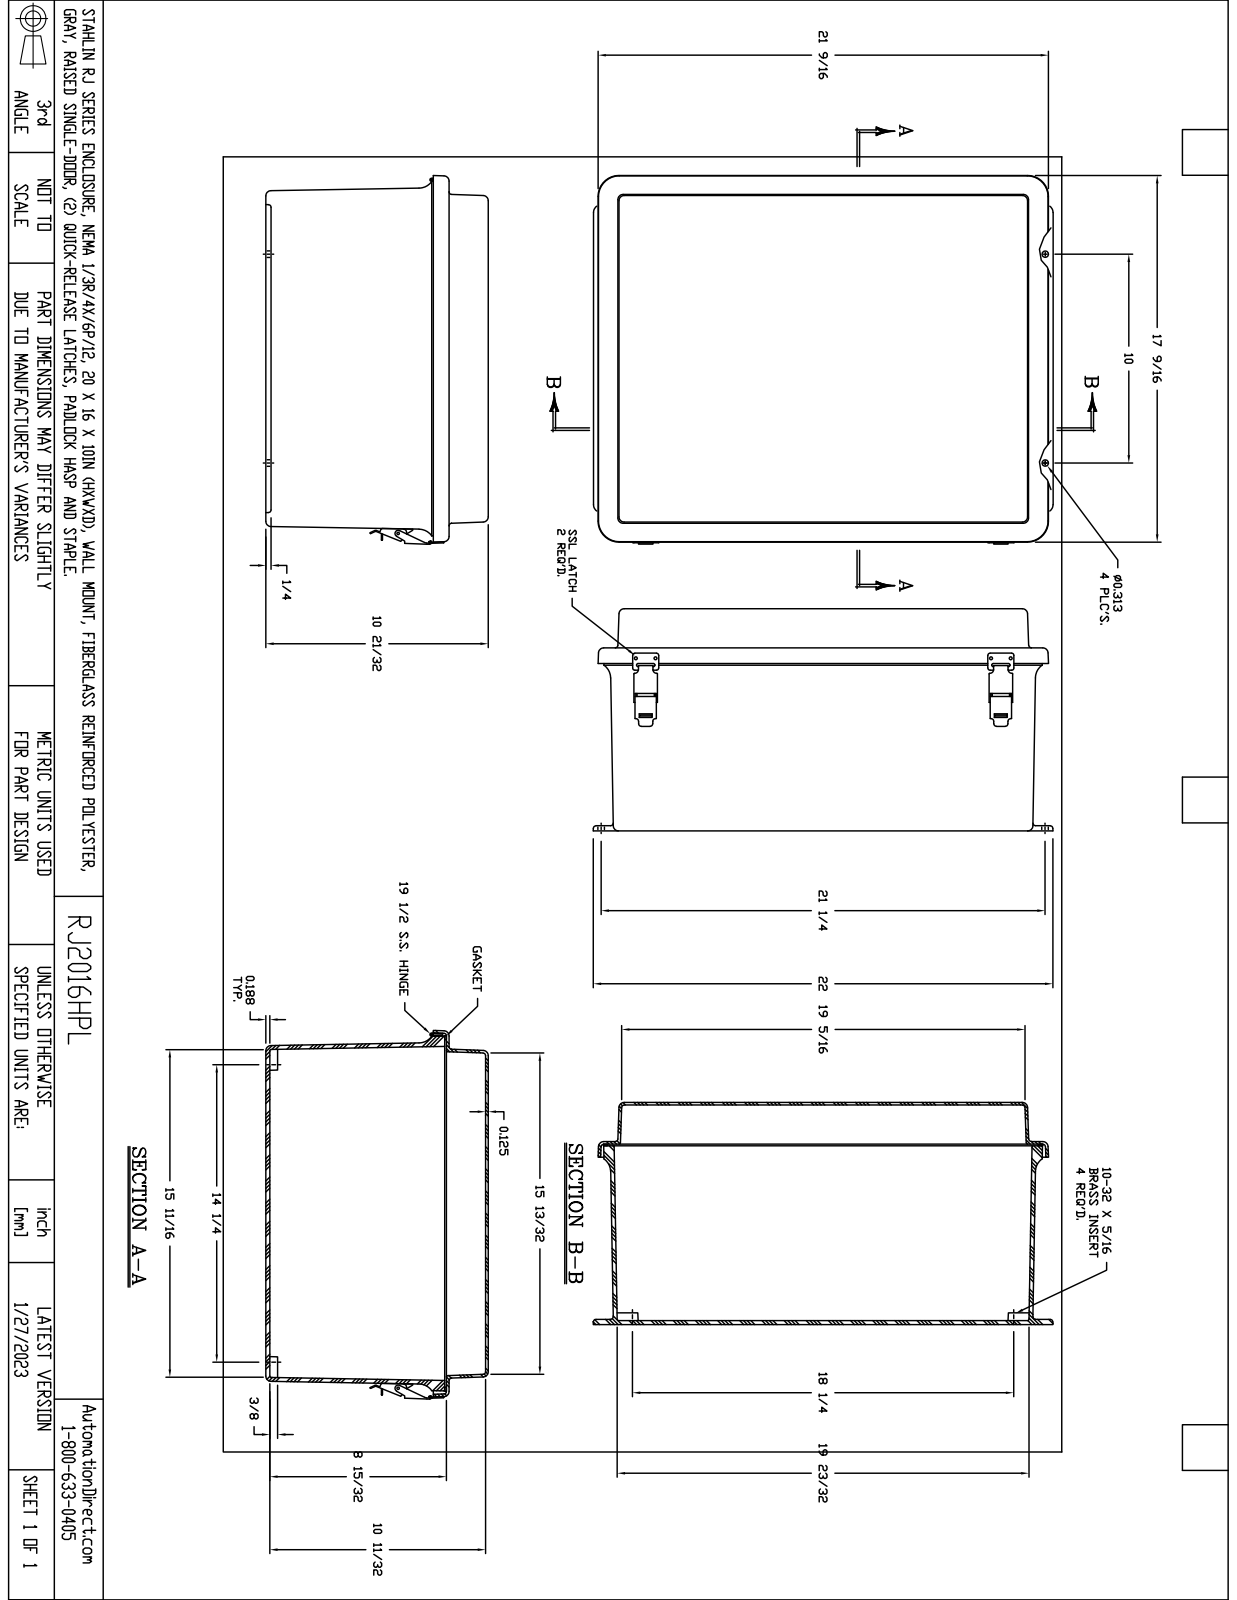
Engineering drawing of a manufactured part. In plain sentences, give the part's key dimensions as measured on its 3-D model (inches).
The part is named "MR2016HPL". Its 3-D file was written by "SolidWorks 2018 (AUTOMOTIVE_DESIGN)". It is 42 solids with 1215 faces: 543 planar, 505 cylindrical and 167 other. Overall it measures 22 by 17.698 by 10.642 inches. Its volume is 271.4 cubic inches and its surface area 3 192 square inches. Round holes: 24 of diameter 0.14, 12 of diameter 0.131, 8 of diameter 0.104, 5 of diameter 0.152, 4 of diameter 0.13, 4 of diameter 0.156, 4 of diameter 0.218, 2 of diameter 0.135, 2 of diameter 0.375, 1 of diameter 0.085, 1 of diameter 0.135. Round bosses or shafts: 14 of diameter 0.125, 12 of diameter 0.25, 6 of diameter 0.125, 4 of diameter 0.27, 1 of diameter 0.3, 1 of diameter 0.17, 1 of diameter 0.155, 1 of diameter 0.12. Partial cylindrical surfaces (rounded edges, fillets, slot ends): 30 of radius 0.125, 20 of radius 0.015, 20 of radius 0.031, 16 of radius 0.045, 12 of radius 0.03, 12 of radius 0.25, 8 of radius 0.023, 6 of radius 0.06. The main face-to-face distances are 0.187, 0.125, 0.188, 10.517, 10.329, 10.642, 10.454, 8.642, 8.454, 1.875. The hole center spacings are 3.75, 17, 7.5, 0.937, 0.25, 3.5, 4, 7.25.
